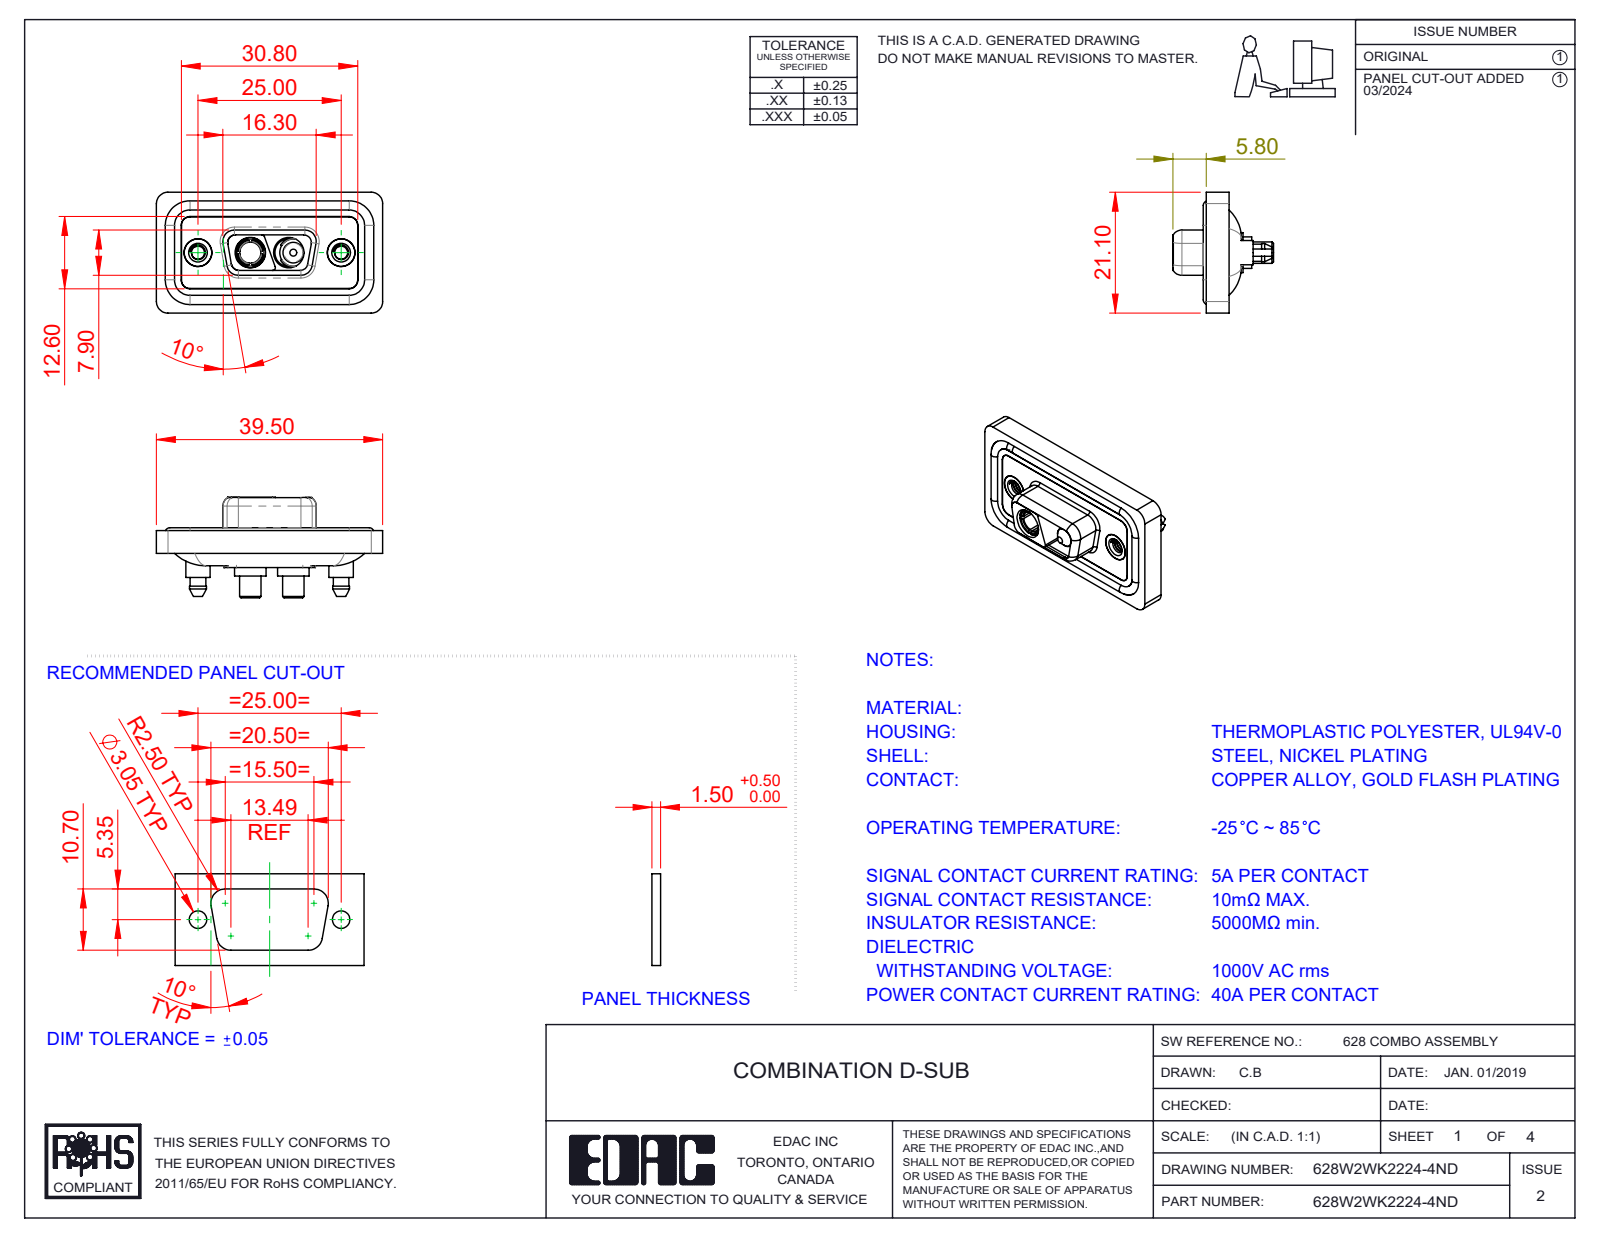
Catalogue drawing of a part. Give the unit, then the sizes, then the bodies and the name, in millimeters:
Units: millimetres
Overall size (bounding box): 39.5 × 21.1 × 17.55
Round holes (diameter × count): ⌀4.85 ×4, ⌀2.26 ×2, ⌀4 ×2, ⌀4.05 ×2, ⌀5 ×2, ⌀5.3 ×2, ⌀3.7 ×1
Round bosses / shafts (diameter × count): ⌀1.6 ×4, ⌀5.5 ×2, ⌀5.4 ×2, ⌀5.2 ×2, ⌀4.95 ×2, ⌀4.8 ×2, ⌀4.75 ×2, ⌀4.25 ×2
Partial cylindrical surfaces — rounded edges, fillets, slot ends (radius × count): R1.5 ×24, R2 ×18, R1.6 ×10, R1.35 ×8, R0.5 ×6, R0.25 ×4, R0.6 ×4, R0.65 ×4
Main face-to-face distances: 0.4, 1.1, 2.9, 1.6, 0.5, 1.8, 5.65, 4, 1.5, 5.35
Hole centre spacings: 9.14, 15.86, 6.72, 25
Volume: 4 775 mm³ · Surface area: 7 705 mm²
Bodies: 11 solids, 566 faces (160 planar, 279 cylindrical, 127 other)
Part name (STEP PRODUCT): 628W2WK2224-4ND; Power Socket_40A S; 628Combo Waterproof Housing_09 Contacts; 628Combo Threaded Boardlock_D (+4 more)
STEP written by: SolidWorks 2023 (CONFIG_CONTROL_DESIGN)
